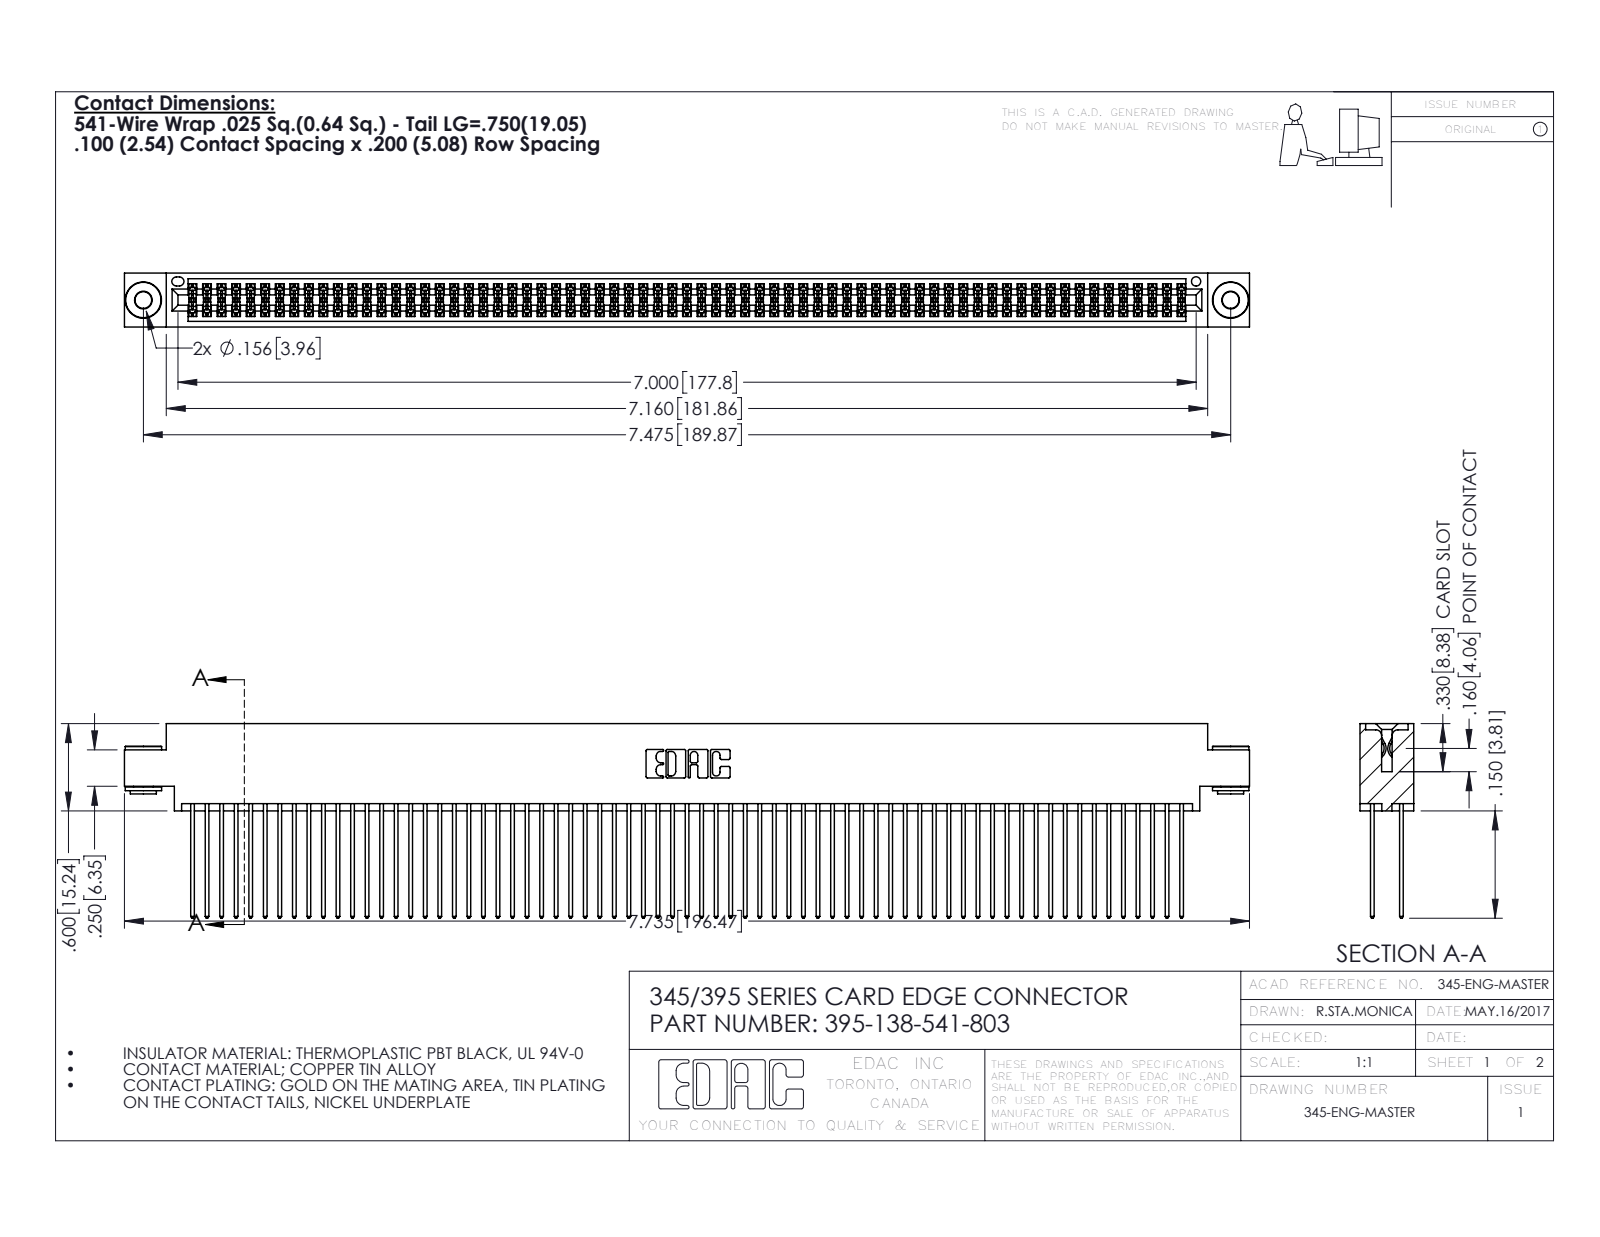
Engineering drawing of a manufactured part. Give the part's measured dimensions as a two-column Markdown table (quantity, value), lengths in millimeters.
| quantity | value |
| --- | --- |
| part name | 345 Part_0.170 Offset - 0.156 Dia-TH; 345-250-002_345-250-002-102; 345-292-001_345-293-141; 395-138-541-803 |
| STEP written by | SolidWorks 2016 (CONFIG_CONTROL_DESIGN) |
| units | millimeters |
| bodies | 141 solids, 7068 faces (4648 planar, 2412 cylindrical, 8 other) |
| overall size | 196.5 × 34 × 9.4 |
| volume | 20 040 mm³ |
| surface area | 34 210 mm² |
| round holes (diameter × count) | 2.9 × 2, 4 × 2, 1.6 × 1 |
| round bosses / shafts (diameter × count) | 6.4 × 2, 4.6 × 2, 3.5 × 2 |
| partial cylindrical surfaces (radius × count) | 0.2 × 207, 0.3 × 138, 0.3 × 22, 0.2 × 6, 0.8 × 6, 0.7 × 3, 0.4 × 2, 0.5 × 2 |
| main face-to-face distances | 1.8, 7.6, 5.1, 2.5, 6.9, 0.6, 5.7, 9.4, 4.4, 3.8 |
| hole center spacings | 6.9, 183.9, 189.9 |
